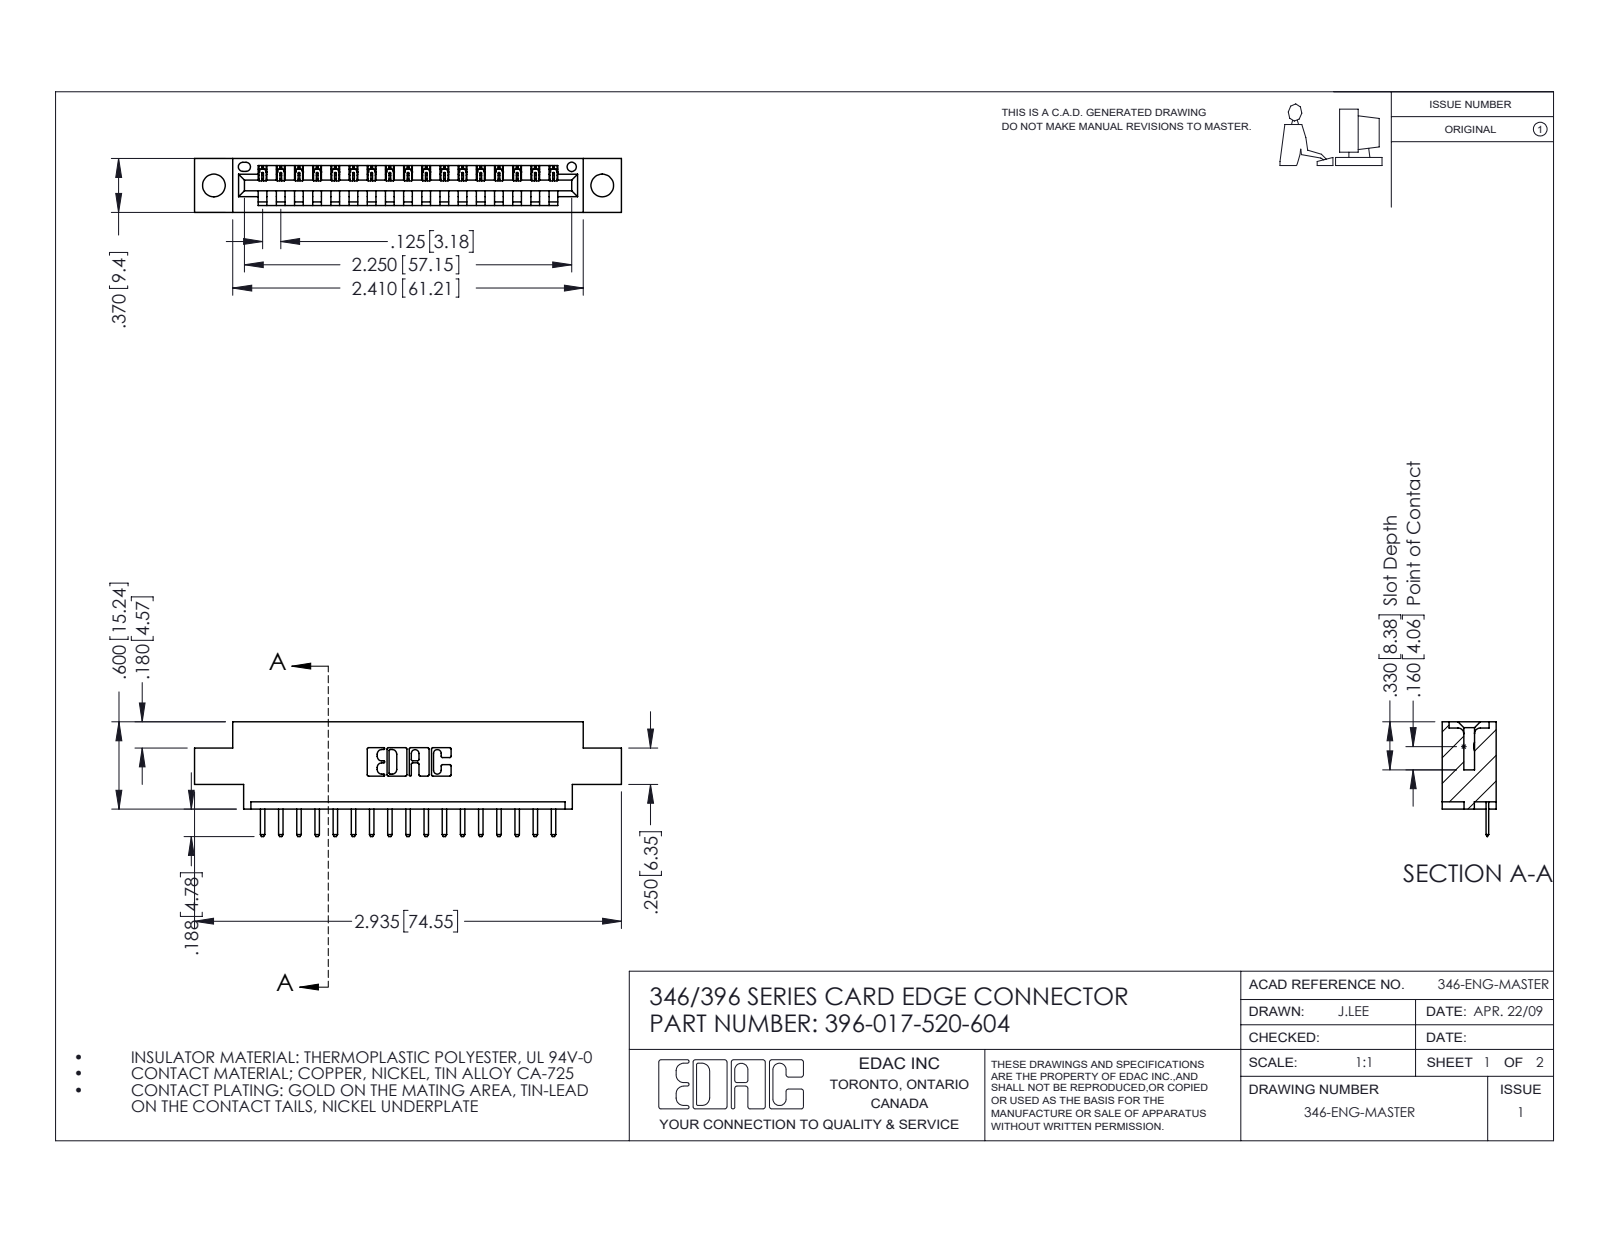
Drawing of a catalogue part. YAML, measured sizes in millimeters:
part_name: "346 Part_0.170 Offset - 0.156 Dia-TH; 396-017-520-604; 345-292-001_345-293-120"
step_written_by: "SolidWorks 2016 (CONFIG_CONTROL_DESIGN)"
units: millimeters
bodies: {solids: 18, faces: 1180, planar: 794, cylindrical: 386, other: 0}
overall_size: [74.5, 20, 9.4]
volume: 6670
surface_area: 7871
round_holes:
  - {diameter: 4, count: 2}
  - {diameter: 1.6, count: 1}
partial_cylinders:
  - {radius: 0.3, count: 36}
  - {radius: 0.2, count: 34}
  - {radius: 0.3, count: 22}
  - {radius: 0.2, count: 6}
  - {radius: 0.8, count: 6}
  - {radius: 0.7, count: 3}
  - {radius: 0.8, count: 2}
  - {radius: 1, count: 2}
face_to_face_distances: [9.4, 1.2, 8.2, 6.4, 3.8, 5.6, 2.5, 4.4, 1.8, 7.6]
hole_center_spacings: [6.2, 62.6, 67.8]
